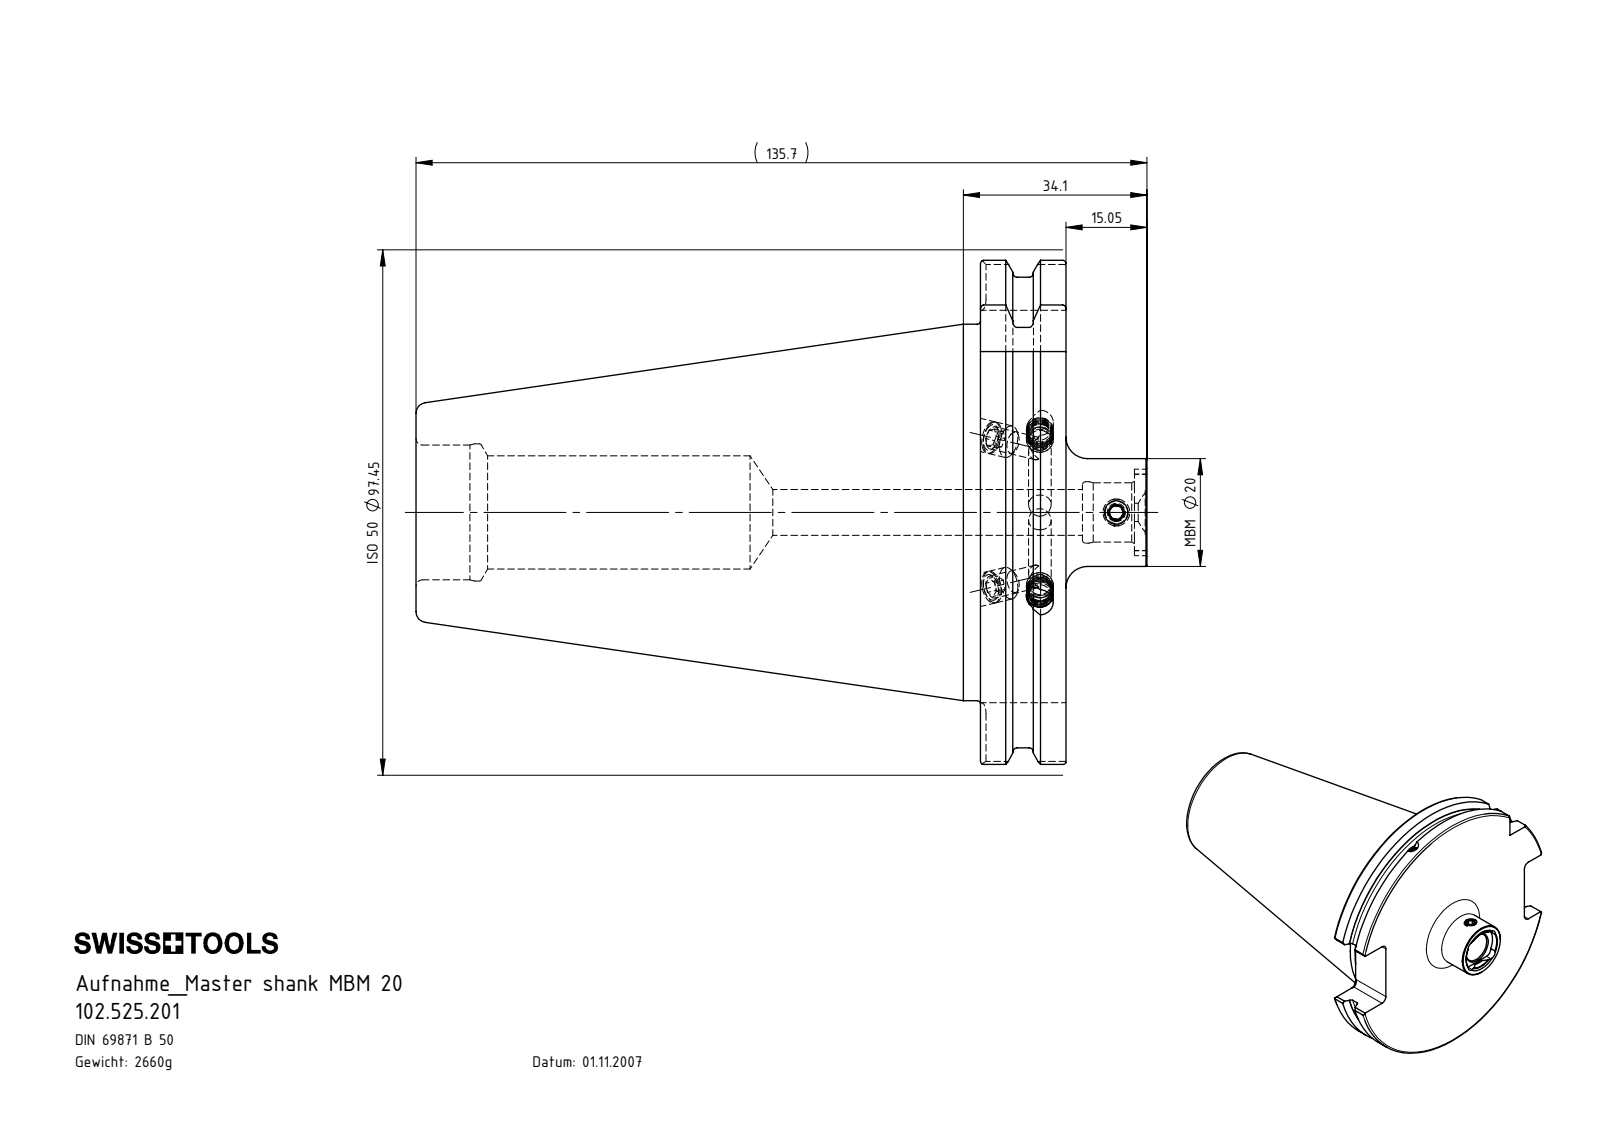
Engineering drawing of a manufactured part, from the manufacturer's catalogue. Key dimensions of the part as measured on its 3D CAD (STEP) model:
Part name (STEP PRODUCT): SB5-MB1.K01.034_C_mit Bundkhlung; MB1-ER1.001.006_A; ISO 4026 - M6 x 5_PreviewCfg; KVT_MB_600_050 (+1 more)
STEP written by: SolidWorks 2017 (CONFIG_CONTROL_DESIGN)
Units: millimetres
Bodies: 8 solids, 298 faces (77 planar, 82 cylindrical, 139 other)
Overall size (bounding box): 135.7 × 97.45 × 93.51
Volume: 339 067 mm³ · Surface area: 44 698 mm²
Round holes (diameter × count): ⌀4.2 ×4, ⌀4 ×2, ⌀6 ×2, ⌀2.5 ×1, ⌀5 ×1, ⌀8.5 ×1, ⌀11 ×1, ⌀11.4 ×1, ⌀21 ×1, ⌀25 ×1, ⌀25.45 ×1
Round bosses / shafts (diameter × count): ⌀6 ×2, ⌀5 ×2, ⌀91 ×1, ⌀69.85 ×1, ⌀20 ×1
Partial cylindrical surfaces — rounded edges, fillets, slot ends (radius × count): R2 ×8, R2.2 ×4, R6.5 ×1, R8.03 ×1, R48.73 ×1
Main face-to-face distances: 15.85, 104.8, 120.65, 72.8, 25.7, 42.7, 17, 7.65, 65.15, 135.7
